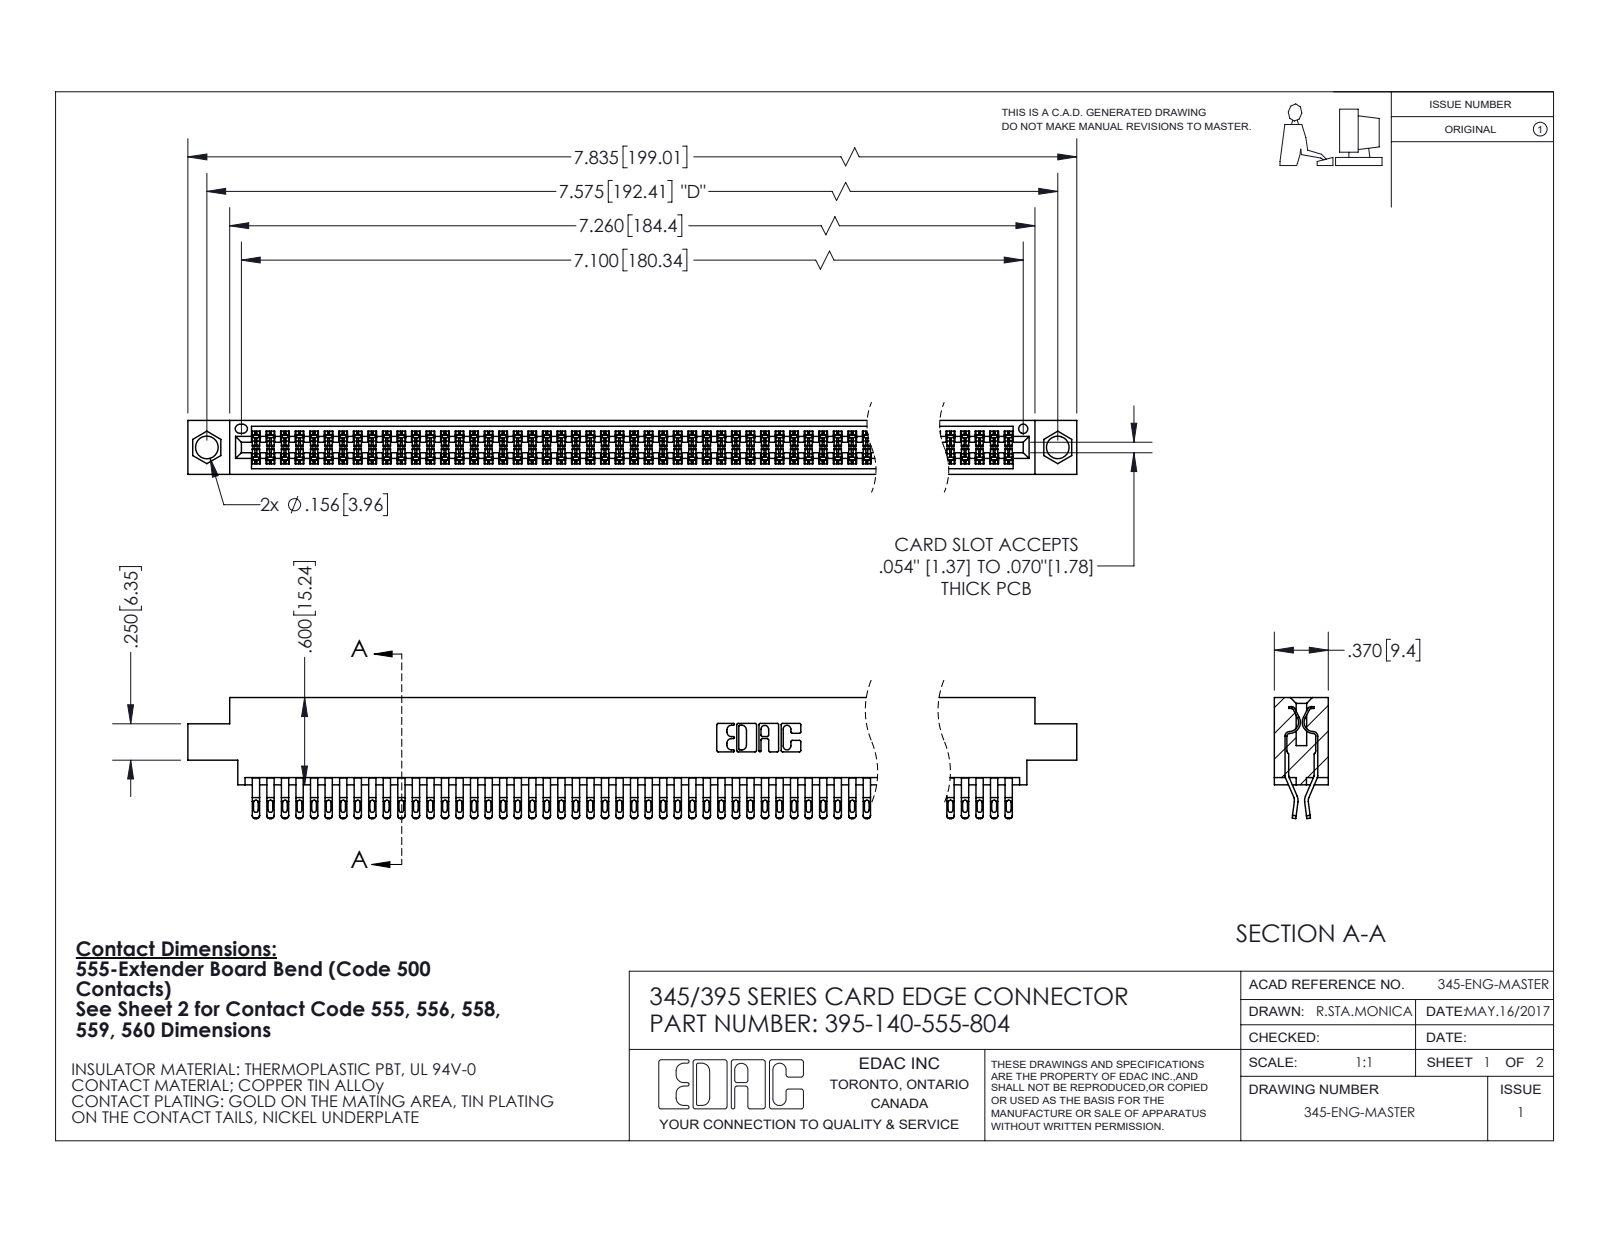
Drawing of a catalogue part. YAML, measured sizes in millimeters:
part_name: "345 Part_0.170 Offset - 0.156 Dia-TI; 395-140-555-804; 345-292-001_555 Tail"
step_written_by: "SolidWorks 2020 (CONFIG_CONTROL_DESIGN)"
units: millimeters
bodies: {solids: 141, faces: 7984, planar: 4438, cylindrical: 3546, other: 0}
overall_size: [199, 21.1, 9.4]
volume: 19780
surface_area: 31190
round_holes:
  - {diameter: 4, count: 2}
  - {diameter: 1.6, count: 1}
partial_cylinders:
  - {radius: 0.4, count: 350}
  - {radius: 0.2, count: 280}
  - {radius: 0.5, count: 280}
  - {radius: 0.3, count: 22}
  - {radius: 0.2, count: 6}
  - {radius: 0.8, count: 6}
  - {radius: 0.7, count: 3}
  - {radius: 0.3, count: 2}
face_to_face_distances: [1.8, 7.6, 0.6, 9.4, 5.1, 2.5, 6.9, 5.7, 4.4, 3.8]
hole_center_spacings: [6.9, 186.4, 192.4]
